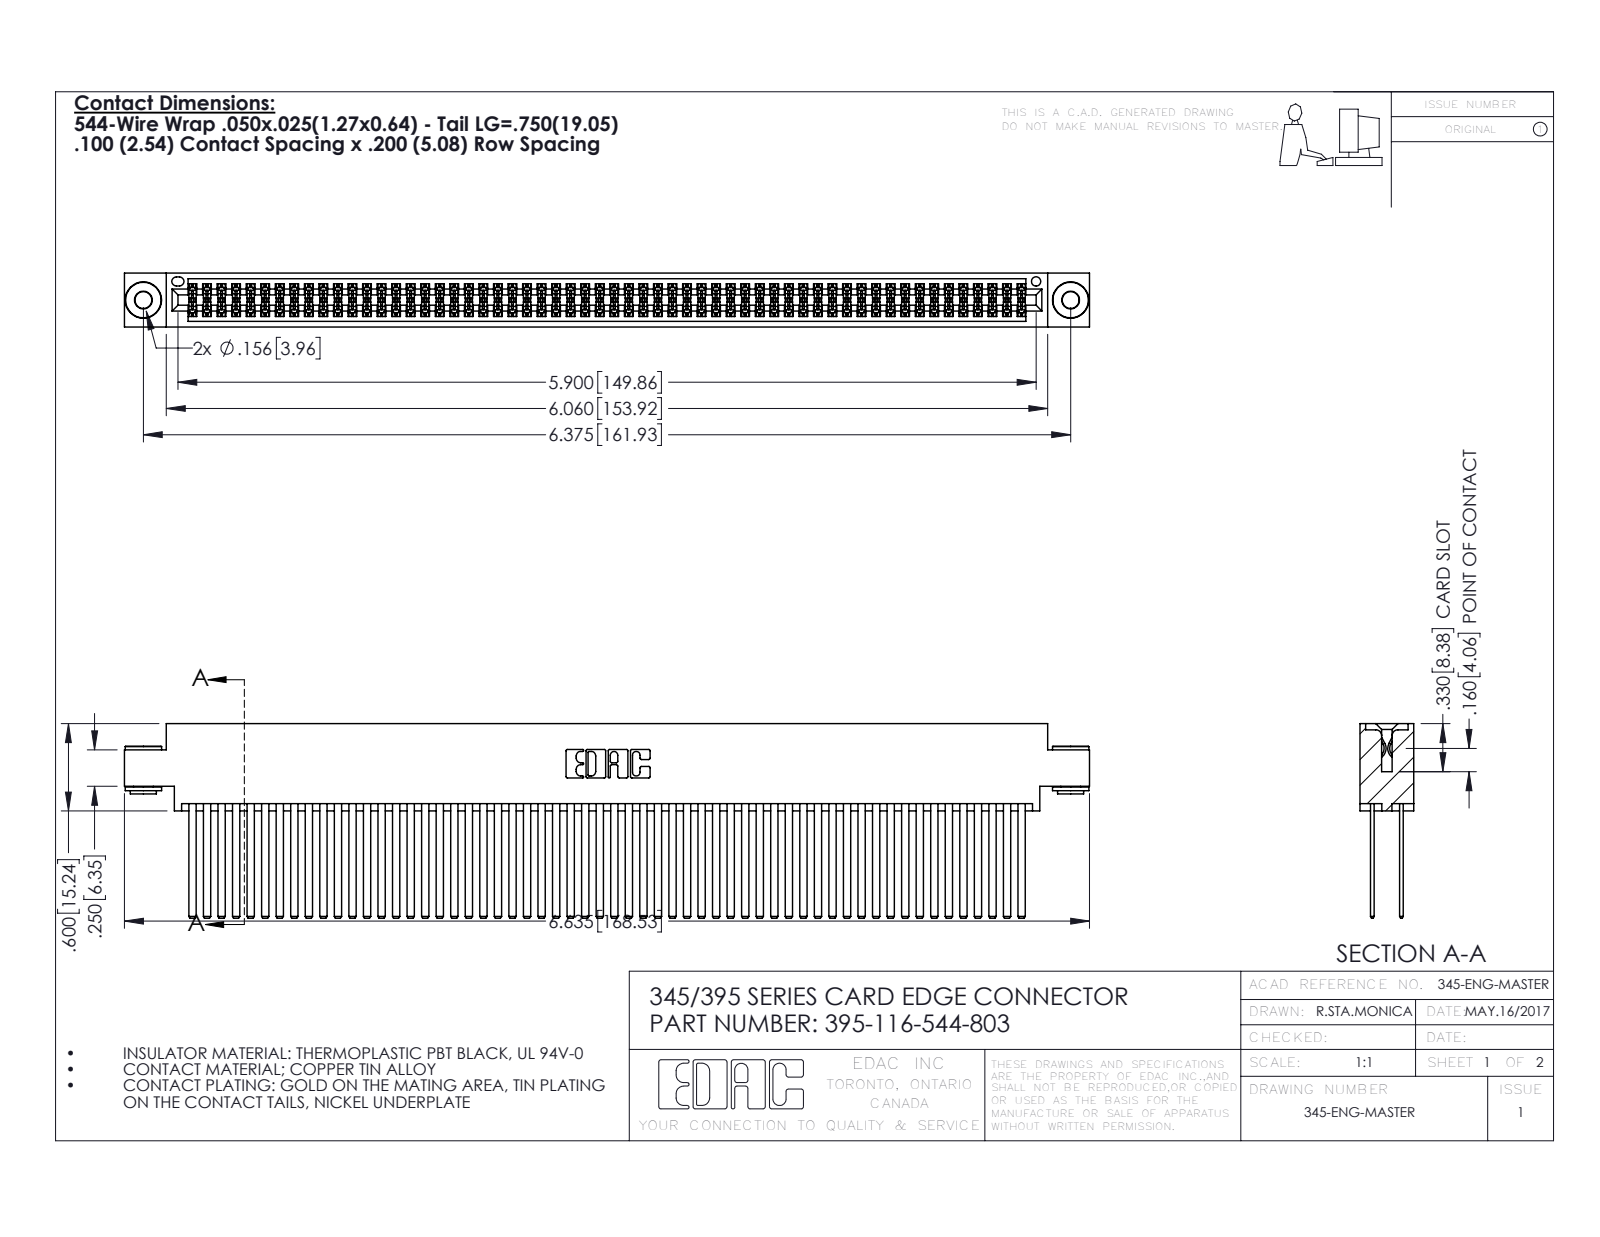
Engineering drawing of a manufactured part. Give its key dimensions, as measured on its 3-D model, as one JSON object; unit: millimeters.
{"part_name": "345-250-002_345-250-002-102; 345-292-001_345-293-144; 345 Part_0.170 Offset - 0.156 Dia-TH; 395-116-544-803", "step_written_by": "SolidWorks 2016 (CONFIG_CONTROL_DESIGN)", "units": "millimeters", "bodies": {"solids": 119, "faces": 5272, "planar": 3458, "cylindrical": 1806, "other": 8}, "overall_size": [168.5, 34, 9.4], "volume_mm3": 18060, "surface_area_mm2": 32110, "round_holes": [[2.9, 2], [4, 2], [1.6, 1]], "round_bosses_or_shafts": [[6.4, 2], [4.6, 2], [3.5, 2]], "partial_cylinders_radius": [[0.2, 174], [0.3, 22], [0.2, 6], [0.8, 6], [0.7, 3], [0.4, 2], [0.5, 2], [0.6, 2]], "face_to_face_distances": [5.1, 0.6, 1.8, 2.5, 6.9, 7.6, 5.7, 4.4, 9.4, 3.8], "hole_center_spacings": [6.9, 155.9, 161.9]}
